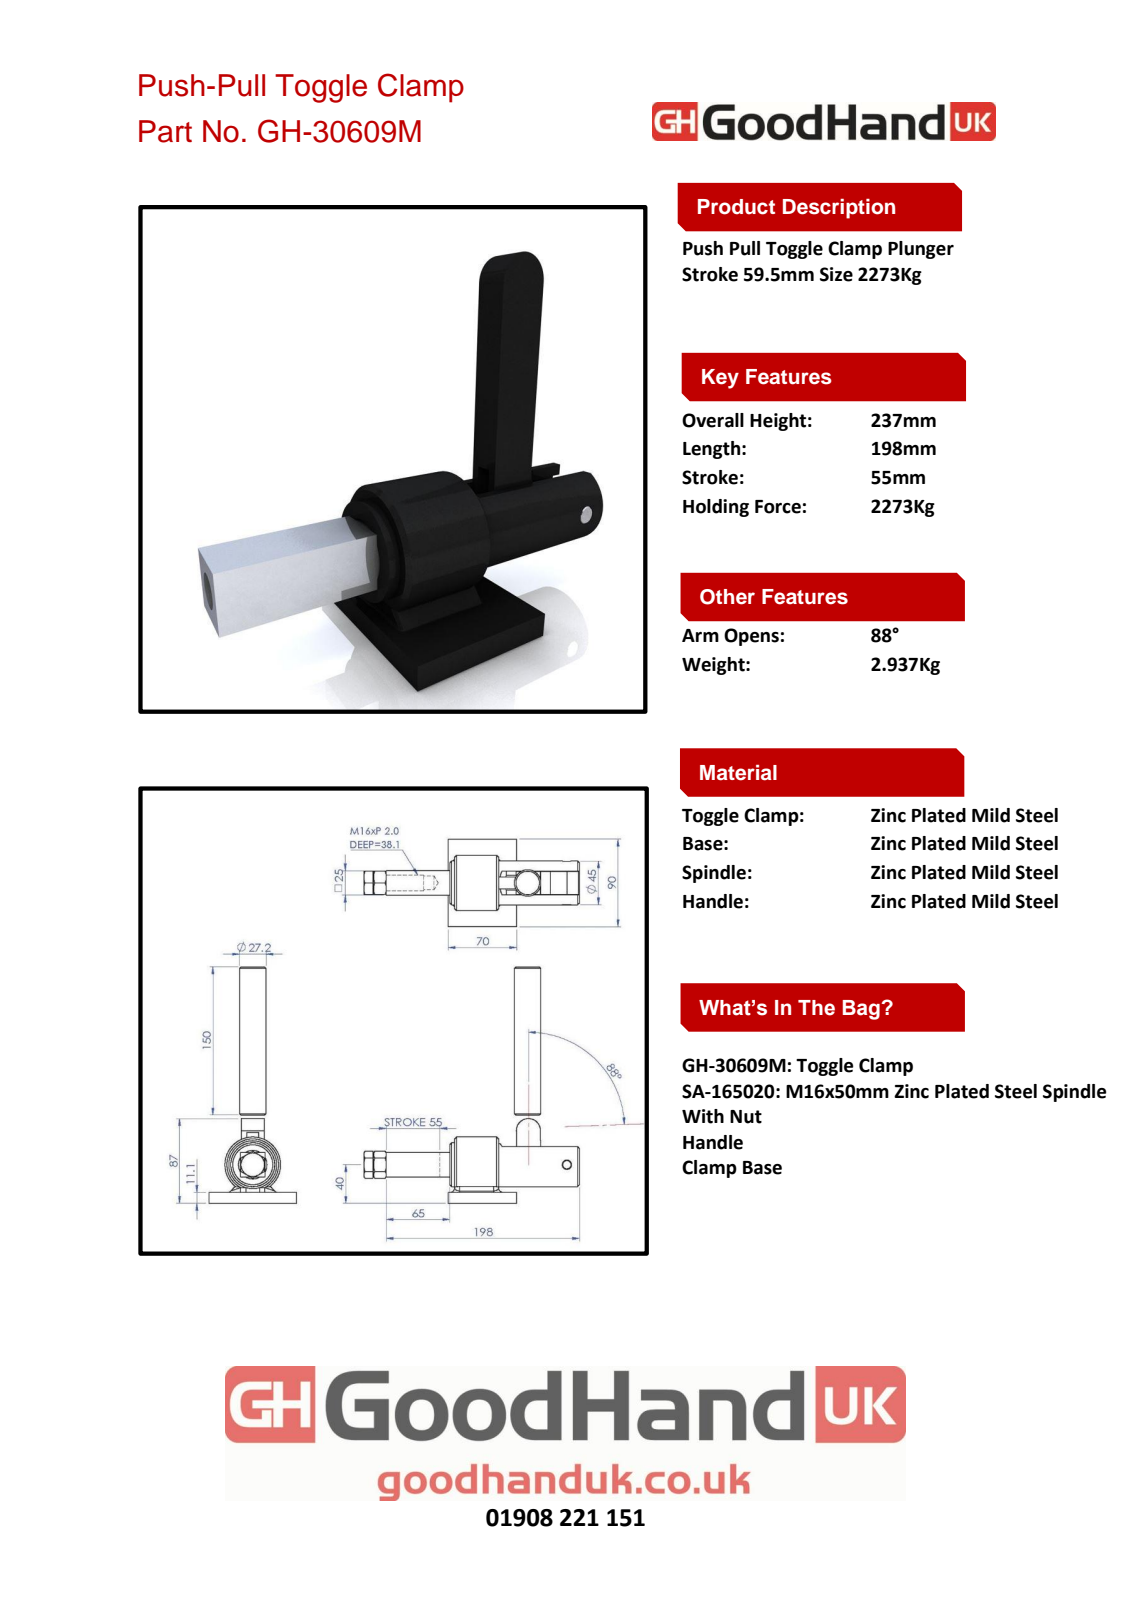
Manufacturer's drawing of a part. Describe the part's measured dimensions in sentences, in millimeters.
The part is named "GH-30609M; Continuous Thread Hexagon Head Bolt_A_JIS_JIS B 1180 Continuous thread hexagon head bolt A M16 x 50 --C; Hexagon Nut_2_JIS_JIS B 1181 Hexagon nut - Class 2 Finished M16 --N". Its 3-D file was written by "SolidWorks 2008 (CONFIG_CONTROL_DESIGN)". It is 12 solids with 1260 faces: 882 planar, 296 cylindrical and 82 other. Overall it measures 247.1 by 221 by 90 millimeters. Its volume is 367 135 cubic millimeters and its surface area 130 687 square millimeters. Round holes: 3 of diameter 9.5, 2 of diameter 9.53, 2 of diameter 14, 1 of diameter 16, 1 of diameter 24.2, 1 of diameter 45.1. Round bosses or shafts: 1 of diameter 45, 1 of diameter 27.2, 1 of diameter 24. Partial cylindrical surfaces (rounded edges, fillets, slot ends): 8 of radius 5, 3 of radius 4.8, 2 of radius 10, 2 of radius 12, 1 of radius 7.05, 1 of radius 11.8, 1 of radius 12.33, 1 of radius 14.65. The main face-to-face distances are 25, 18.5, 6.5, 27.1, 11.1, 16, 52.1, 41, 5.85, 17.95. The hole center spacings are 39.24, 52.68, 91.92.
